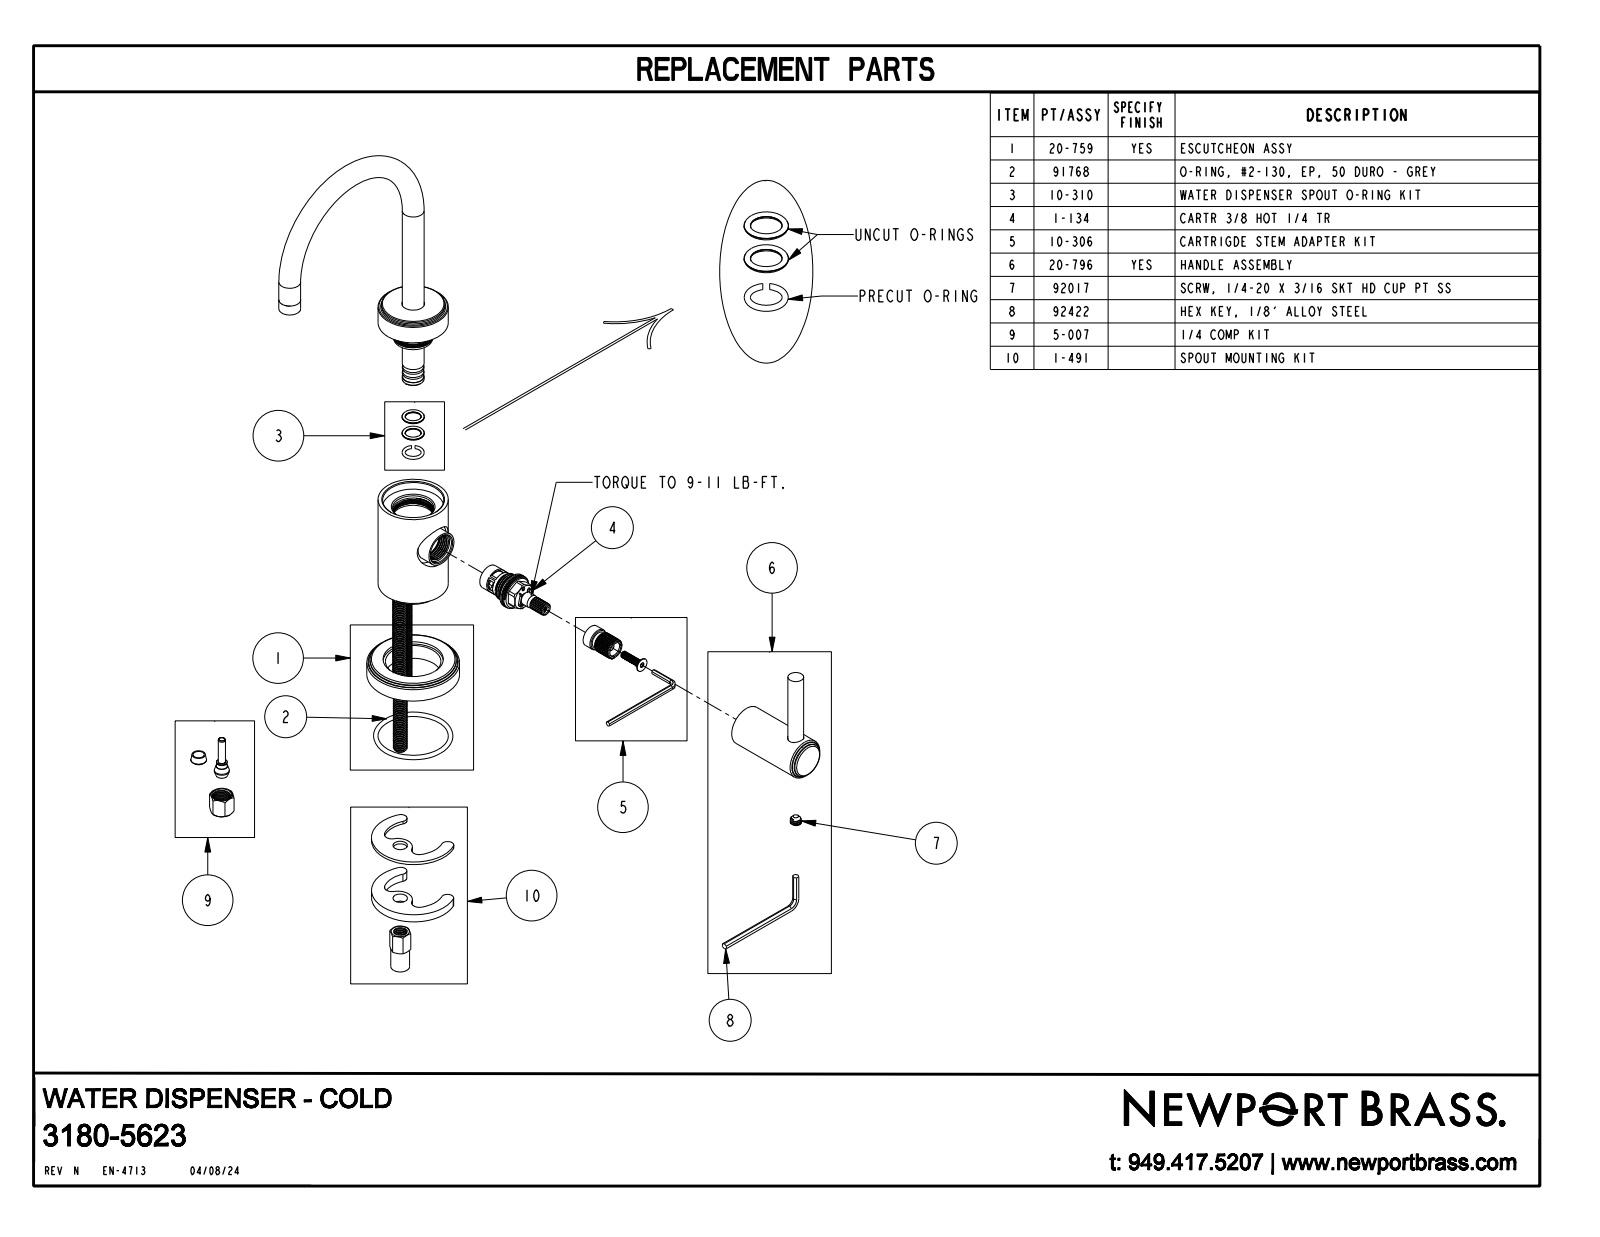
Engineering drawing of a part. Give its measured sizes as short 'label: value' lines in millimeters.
name: 3180-5623
written by: CREO PARAMETRIC BY PTC INC, 2018400 (CONFIG_CONTROL_DESIGN)
unit: mm
bodies: 1 solid, 53 faces (11 planar, 22 cylindrical, 20 other)
size: 234.3 × 135 × 92.7
volume: 175 200 mm³; area: 31 390 mm²
holes: 1× ⌀9.5, 1× ⌀25.4
bosses: 2× ⌀12.7, 1× ⌀54, 1× ⌀50.2, 1× ⌀40.9, 1× ⌀36.8, 1× ⌀24.1, 1× ⌀20.3, 1× ⌀9.1
face distances: 82.7, 10.8, 71.9, 164.4, 153.6, 81.8, 80.6, 69.9, 2, 83.8
